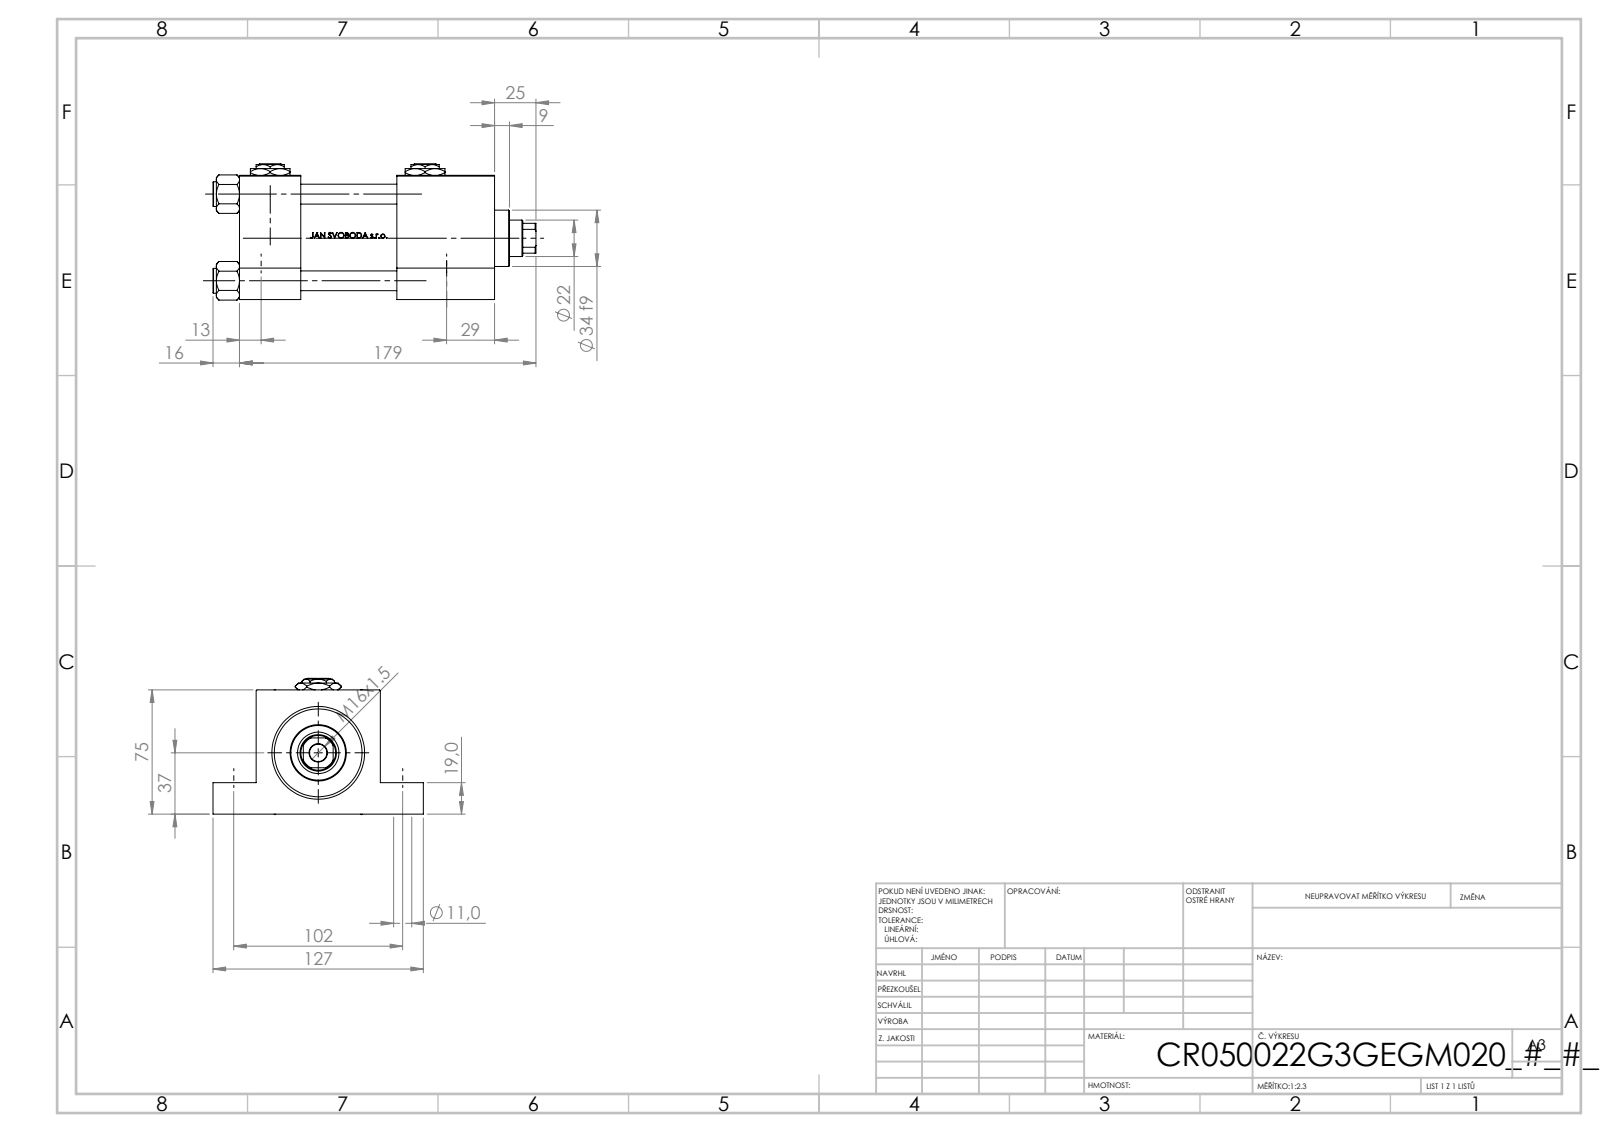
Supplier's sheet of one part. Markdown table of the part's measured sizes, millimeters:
| quantity | value |
| --- | --- |
| part name | V215CR_G_TYCINKA; Zatka_pro_OIL_PORT; V215_VC_A; V215CR_VCP_G (+2 more) |
| STEP written by | SolidWorks 2019 (CONFIG_CONTROL_DESIGN) |
| units | millimeters |
| bodies | 17 solids, 1252 faces (496 planar, 136 cylindrical, 620 other) |
| overall size | 195 × 127 × 82.27 |
| volume | 791 785 mm³ |
| surface area | 176 375 mm² |
| round holes (diameter × count) | 12 × 4, 14 × 4, 7 × 2, 20.96 × 2, 30 × 2, 10.5 × 1, 22 × 1, 25 × 1, 41 × 1, 50 × 1, 53 × 1 |
| round bosses / shafts (diameter × count) | 15 × 4, 56 × 1, 34 × 1 |
| partial cylindrical surfaces (radius × count) | 10.5 × 1 |
| main face-to-face distances | 75, 37, 154, 117, 19, 95, 56, 58, 59, 26 |
| hole center spacings | 36.98, 52.3, 51.3, 52.63, 73.96, 102, 111.36, 112 |
